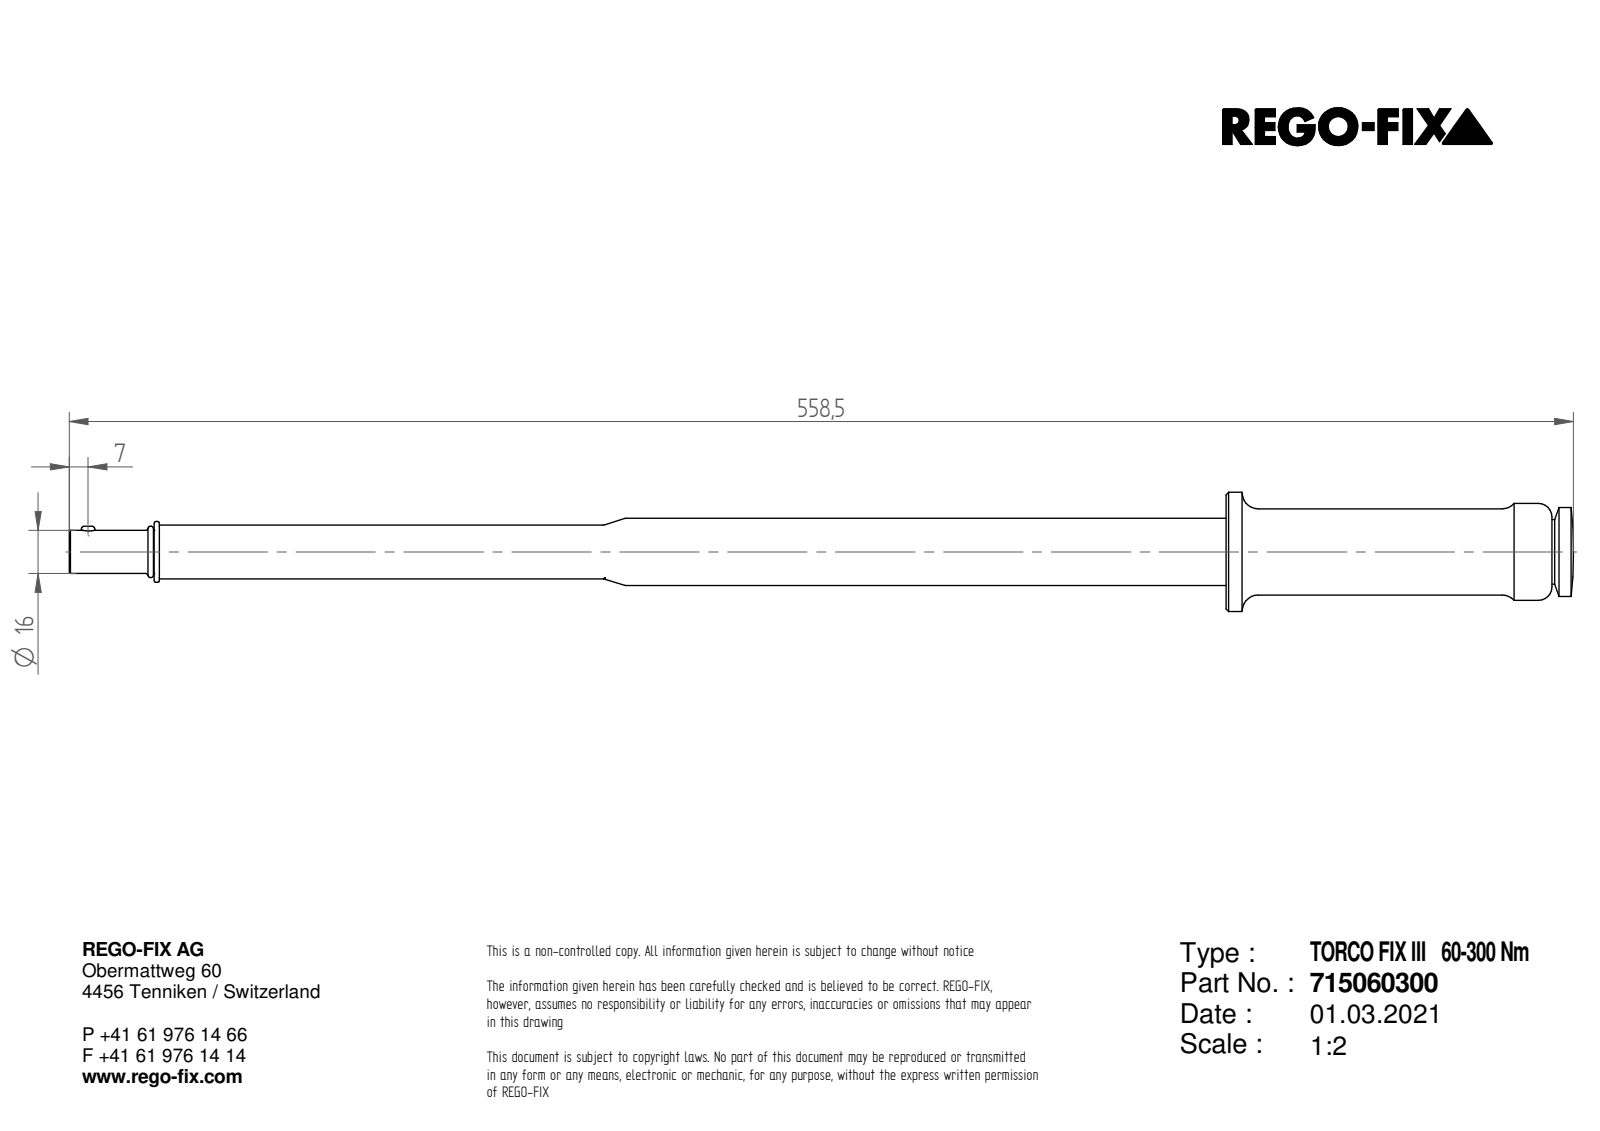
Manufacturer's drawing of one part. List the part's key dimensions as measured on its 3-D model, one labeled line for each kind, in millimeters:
Part name (STEP PRODUCT): 6402-1 TORCO-FIX III Adjustable Torque Wrench 60-300 Nm (16mm interface); 6402-2 TORCO-FIX III Adjustable Torque Wrench 60-300 Nm (16mm interface); 6402 TORCO-FIX III Adjustable Torque Wrench 60-300 Nm (16mm interface )
STEP written by: Alibre (AUTOMOTIVE_DESIGN)
Units: millimetres
Bodies: 2 solids, 57 faces (18 planar, 19 cylindrical, 20 other)
Overall size (bounding box): 558.52 × 44.3 × 44.3
Volume: 333 934 mm³ · Surface area: 56 524 mm²
Round bosses / shafts (diameter × count): ⌀44.3 ×1, ⌀36 ×1, ⌀33 ×1, ⌀32 ×1, ⌀25 ×1, ⌀24 ×1, ⌀22.6 ×1, ⌀19 ×1
Partial cylindrical surfaces — rounded edges, fillets, slot ends (radius × count): R2 ×5, R20 ×1
Main face-to-face distances: 20, 2, 18, 429.5, 31.5, 398, 33.5, 396, 550.5, 519
